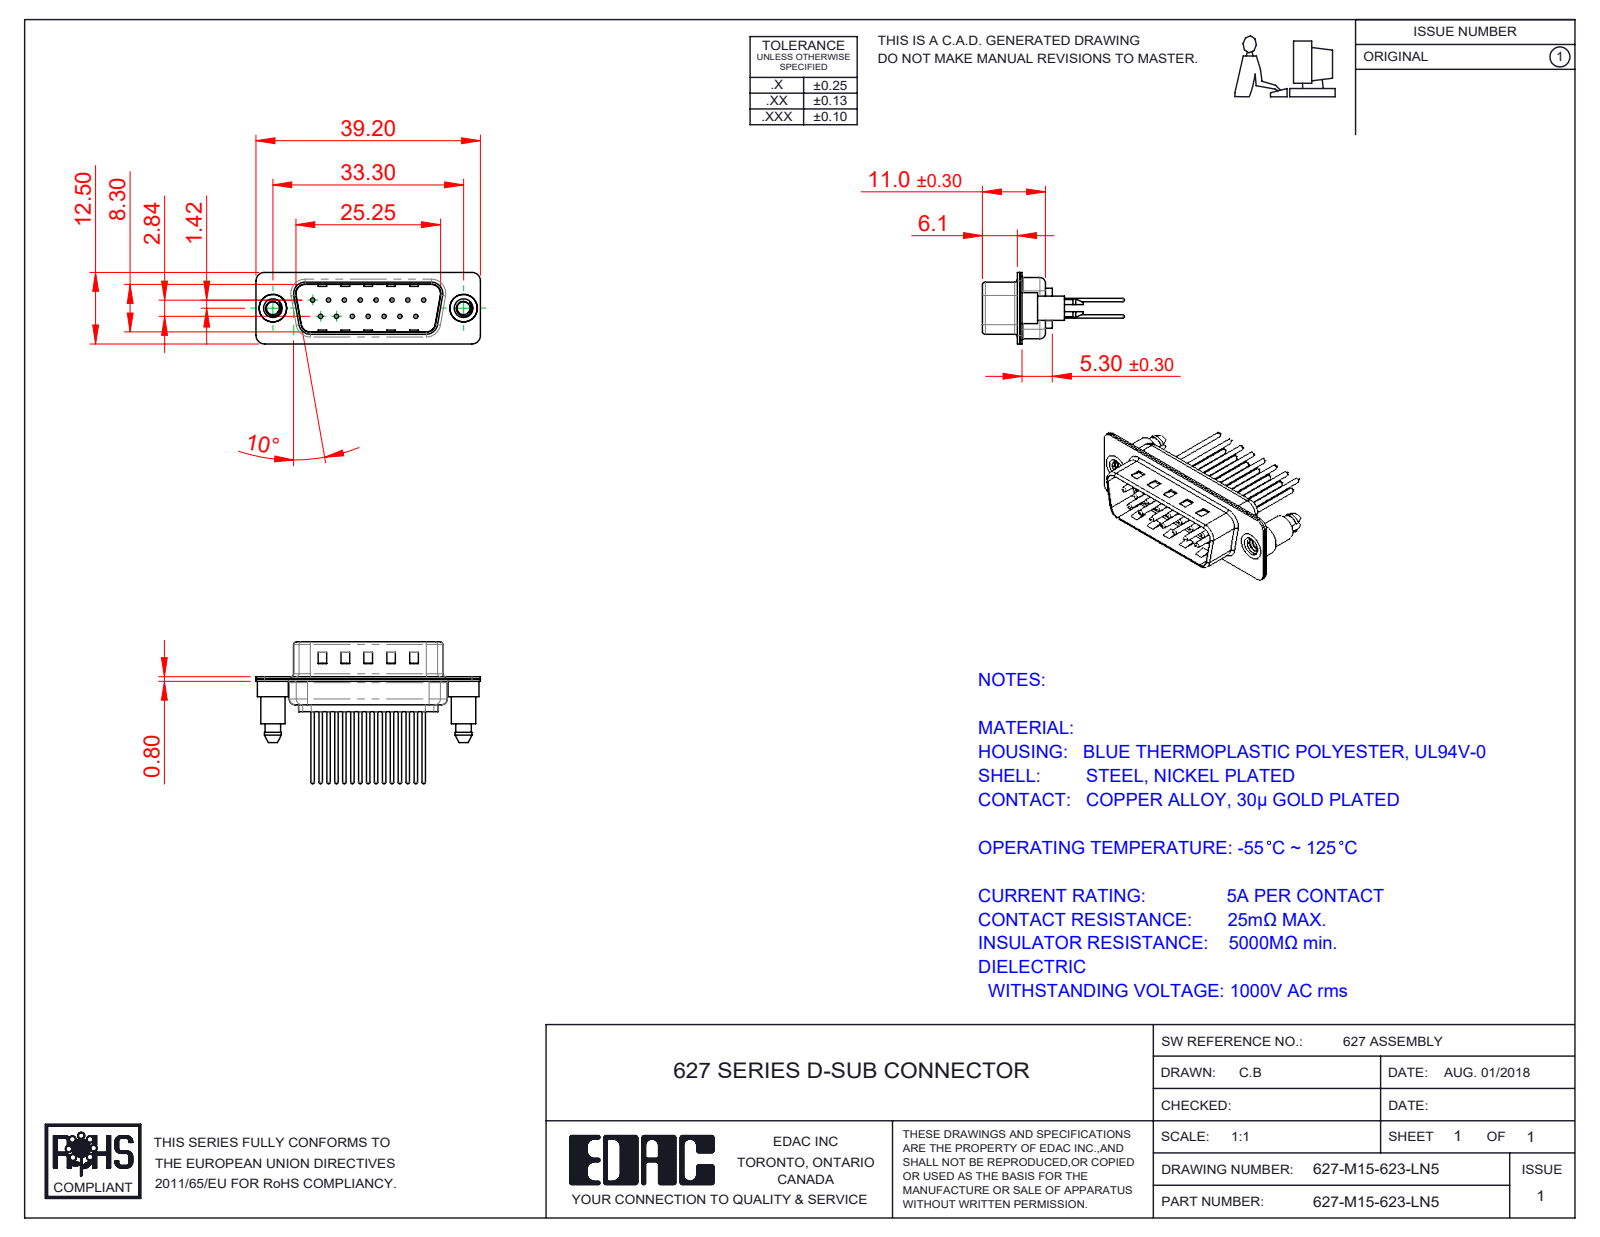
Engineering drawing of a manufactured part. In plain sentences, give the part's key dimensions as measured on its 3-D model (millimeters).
The part is named "627M Shell Rear_15 Contacts; 627M Contact Row 2_23; 627-M15-623-LN5; 627M Housing_15 Contacts (+3 more)". Its 3-D file was written by "SolidWorks 2020 (CONFIG_CONTROL_DESIGN)". It is 20 solids with 945 faces: 260 planar, 375 cylindrical and 310 other. Overall it measures 39.2 by 24.77 by 12.5 millimeters. Its volume is 2 006 cubic millimeters and its surface area 5 336 square millimeters. Round holes: 15 of diameter 0.75, 15 of diameter 1.6, 15 of diameter 2, 2 of diameter 2.26, 2 of diameter 4, 2 of diameter 4.8. Round bosses or shafts: 15 of diameter 1.5, 15 of diameter 0.6, 2 of diameter 5.4, 2 of diameter 4.9, 2 of diameter 4.25. Partial cylindrical surfaces (rounded edges, fillets, slot ends): 18 of radius 1.5, 12 of radius 2, 10 of radius 1.6, 8 of radius 0.5, 4 of radius 0.25, 4 of radius 0.6, 4 of radius 0.65, 4 of radius 0.9. The main face-to-face distances are 0.4, 0.8, 9.5, 9.1, 8.7, 9.9, 5.3, 1.2, 6.1, 5.7. The hole center spacings are 3.16, 2.77, 5.54, 8.31, 11.08, 5.03, 5.04, 7.48.
